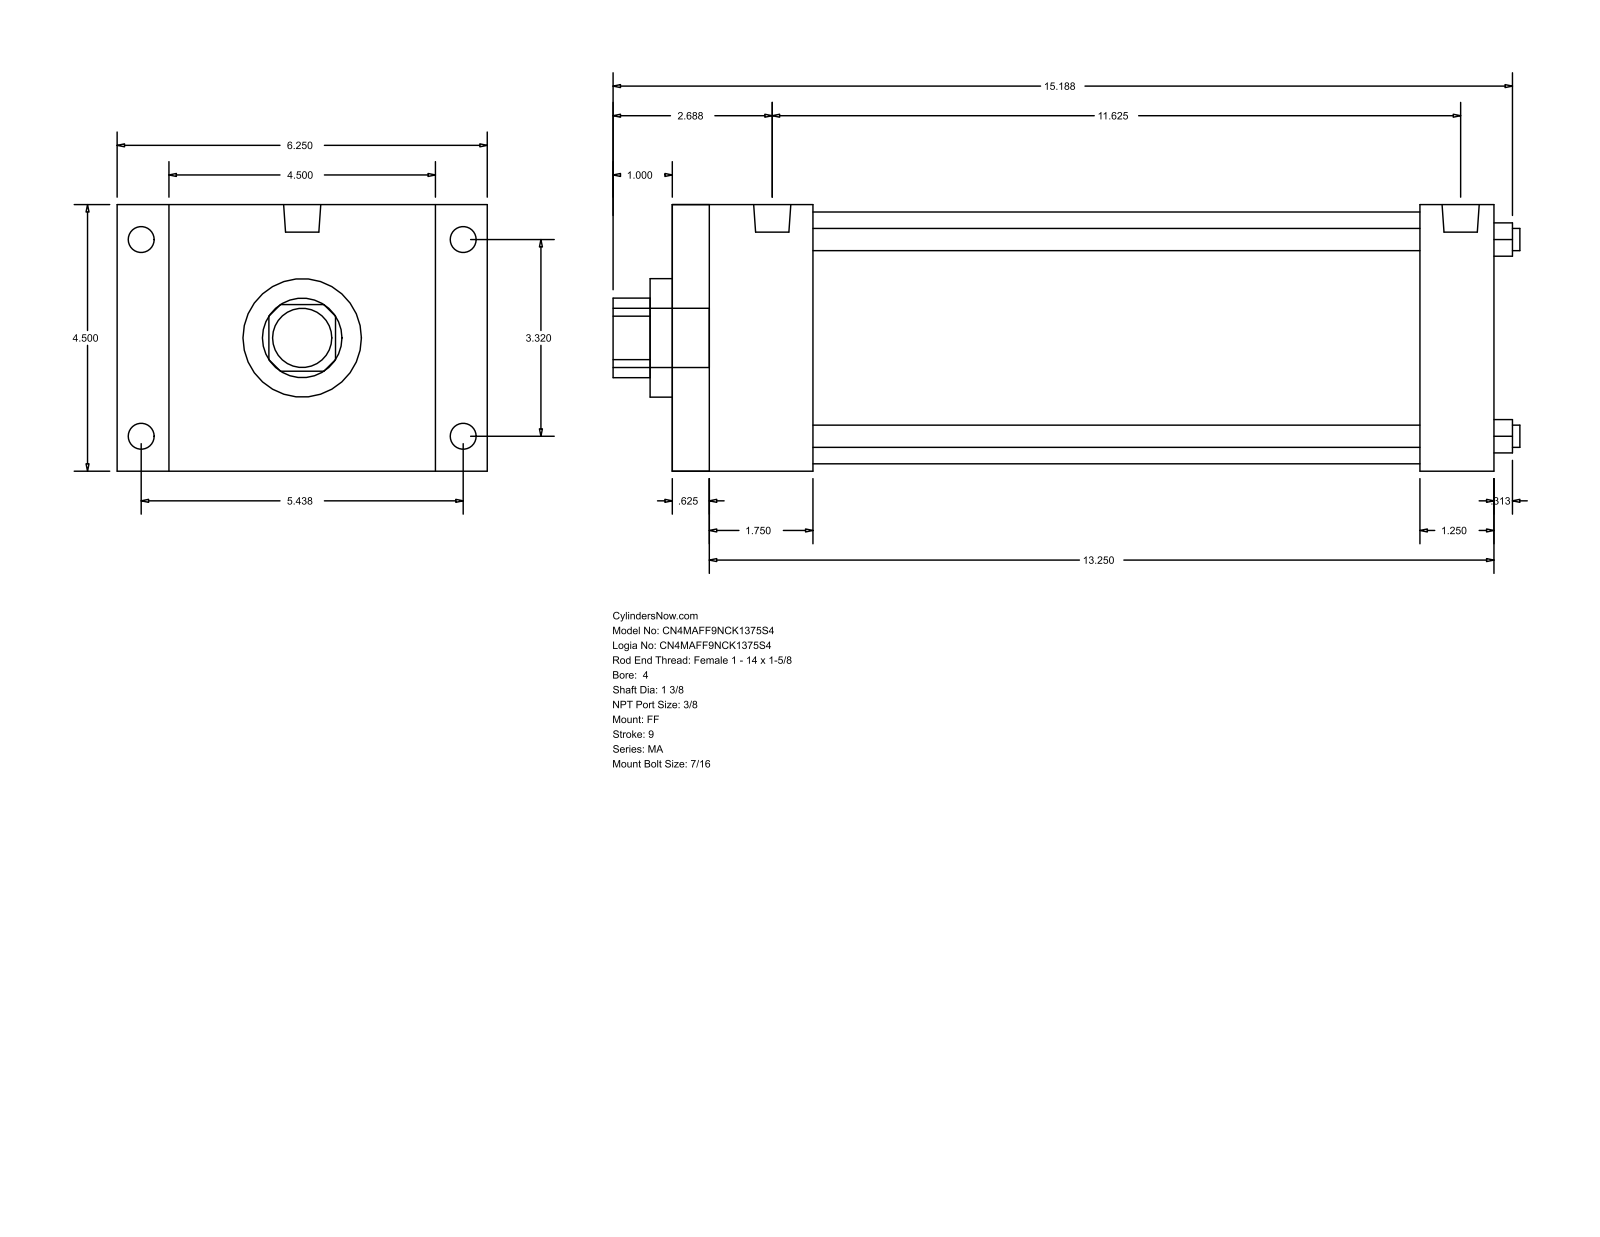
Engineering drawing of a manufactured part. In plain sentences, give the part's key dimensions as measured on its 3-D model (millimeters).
The part is named "MA_FF__0400_1.375". Its 3-D file was written by "GSSL Pune (CONFIG_CONTROL_DESIGN)". It is 0 solids with 92 faces: 64 planar, 28 cylindrical and 0 other. Overall it measures 388.94 by 158.75 by 114.3 millimeters. Round holes: 4 of diameter 9.53, 1 of diameter 34.92, 1 of diameter 50.8, 1 of diameter 107.95. Round bosses or shafts: 8 of diameter 11.11, 2 of diameter 15.93, 1 of diameter 25.4. Partial cylindrical surfaces (rounded edges, fillets, slot ends): 1 of radius 17.06. The main face-to-face distances are 114.3, 352.42, 15.87, 336.55, 22.23, 136.53, 320.67, 304.8, 31.75, 60.32. The hole center spacings are 59.62, 84.32, 119.25.
